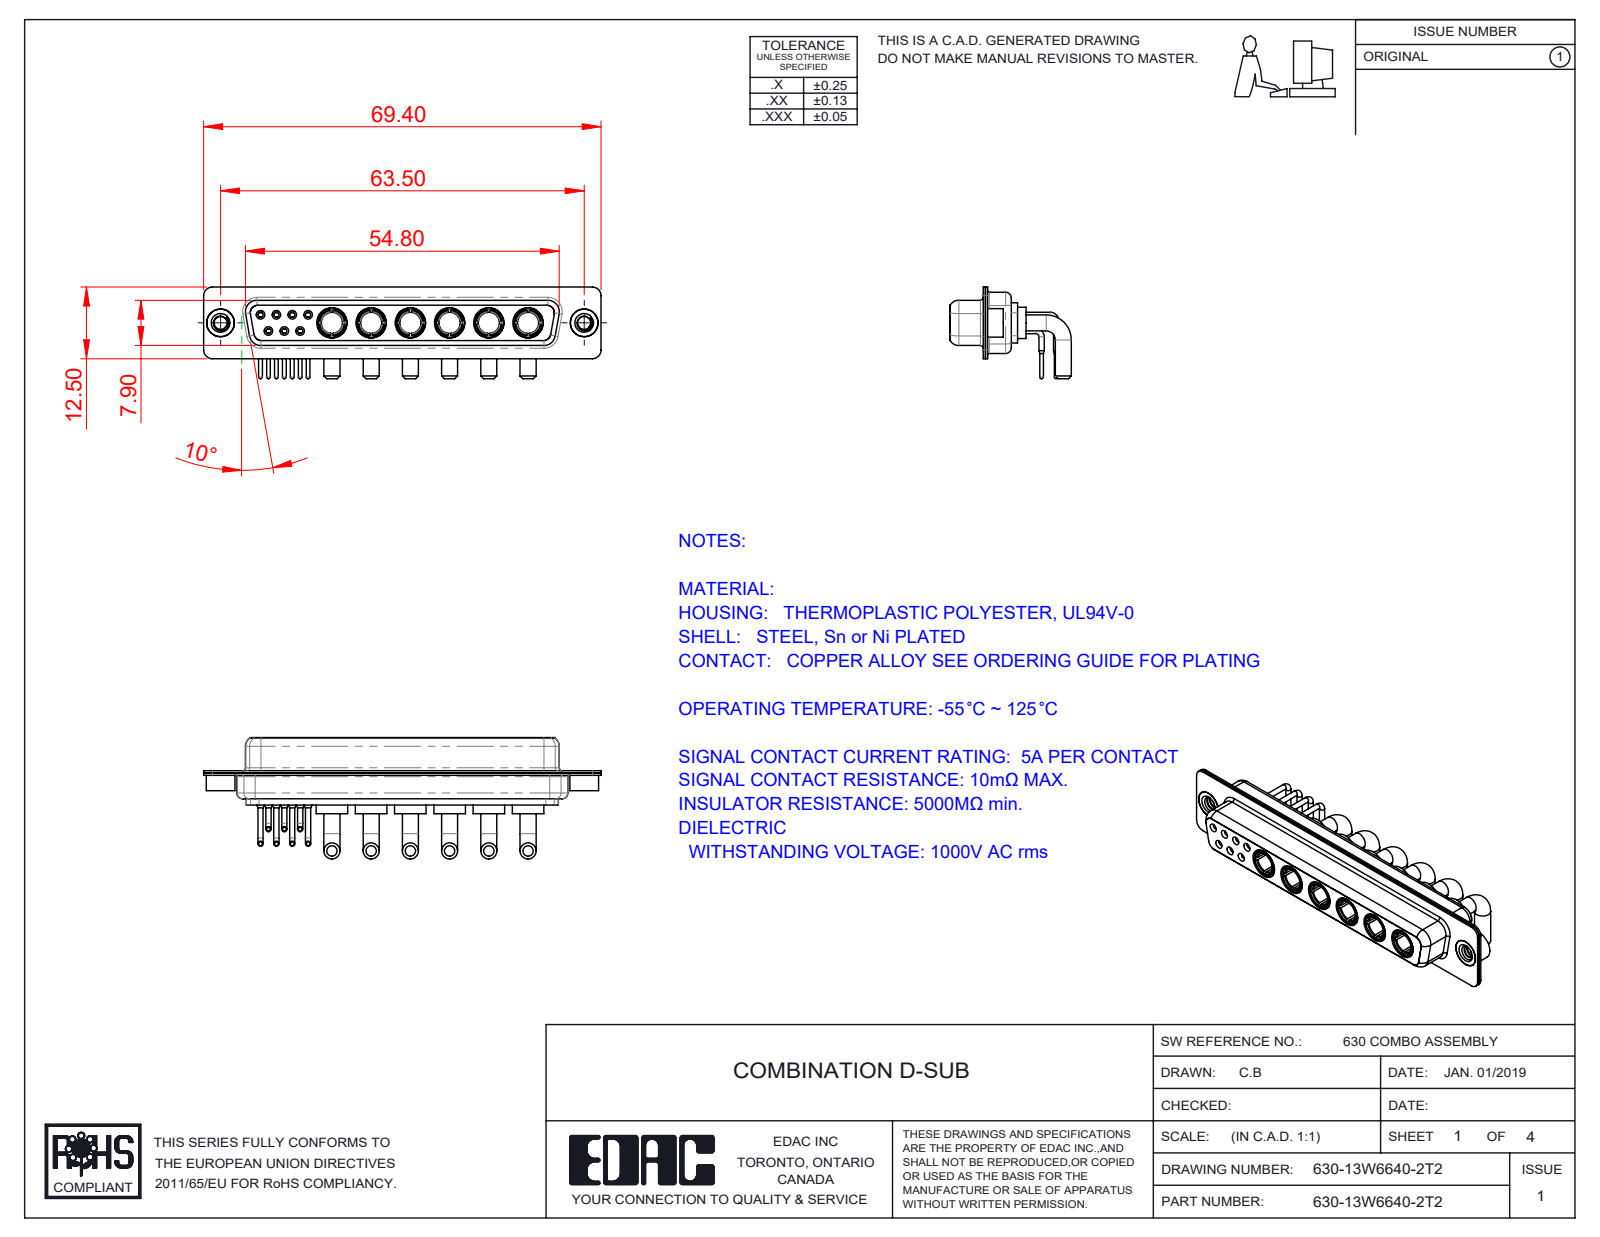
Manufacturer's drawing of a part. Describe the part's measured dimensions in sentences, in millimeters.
The part is named "630-13W6640-2T2; 630Combo Shell Rear_37 Contacts; 630Combo Housing_13W6; Power Socket_20A RA (+4 more)". Its 3-D file was written by "SolidWorks 2020 (CONFIG_CONTROL_DESIGN)". It is 24 solids with 1118 faces: 346 planar, 448 cylindrical and 324 other. Overall it measures 69.4 by 21.2 by 16 millimeters. Its volume is 5 676 cubic millimeters and its surface area 12 226 square millimeters. Round holes: 8 of diameter 4.85, 7 of diameter 0.9, 7 of diameter 1.1, 7 of diameter 1.5, 7 of diameter 2, 6 of diameter 3.7, 6 of diameter 5.3, 4 of diameter 1.7, 3 of diameter 1.6, 2 of diameter 2.26, 2 of diameter 4, 2 of diameter 4.05. Round bosses or shafts: 12 of diameter 2.8, 7 of diameter 0.9, 7 of diameter 0.65, 6 of diameter 5.5, 6 of diameter 5.2, 6 of diameter 4.96, 6 of diameter 4.75, 6 of diameter 3.75. Partial cylindrical surfaces (rounded edges, fillets, slot ends): 16 of radius 1.5, 12 of radius 2, 8 of radius 1.35, 8 of radius 1.6, 6 of radius 2.1, 4 of radius 0.25, 4 of radius 0.5, 4 of radius 0.6. The main face-to-face distances are 0.4, 1.4, 0.45, 8.45, 8.9, 1.8, 7.05, 6.2, 7.5, 1.85. The hole center spacings are 3.16, 2.77, 6.85, 13.7, 5.54, 20.55, 5.03, 5.04.
